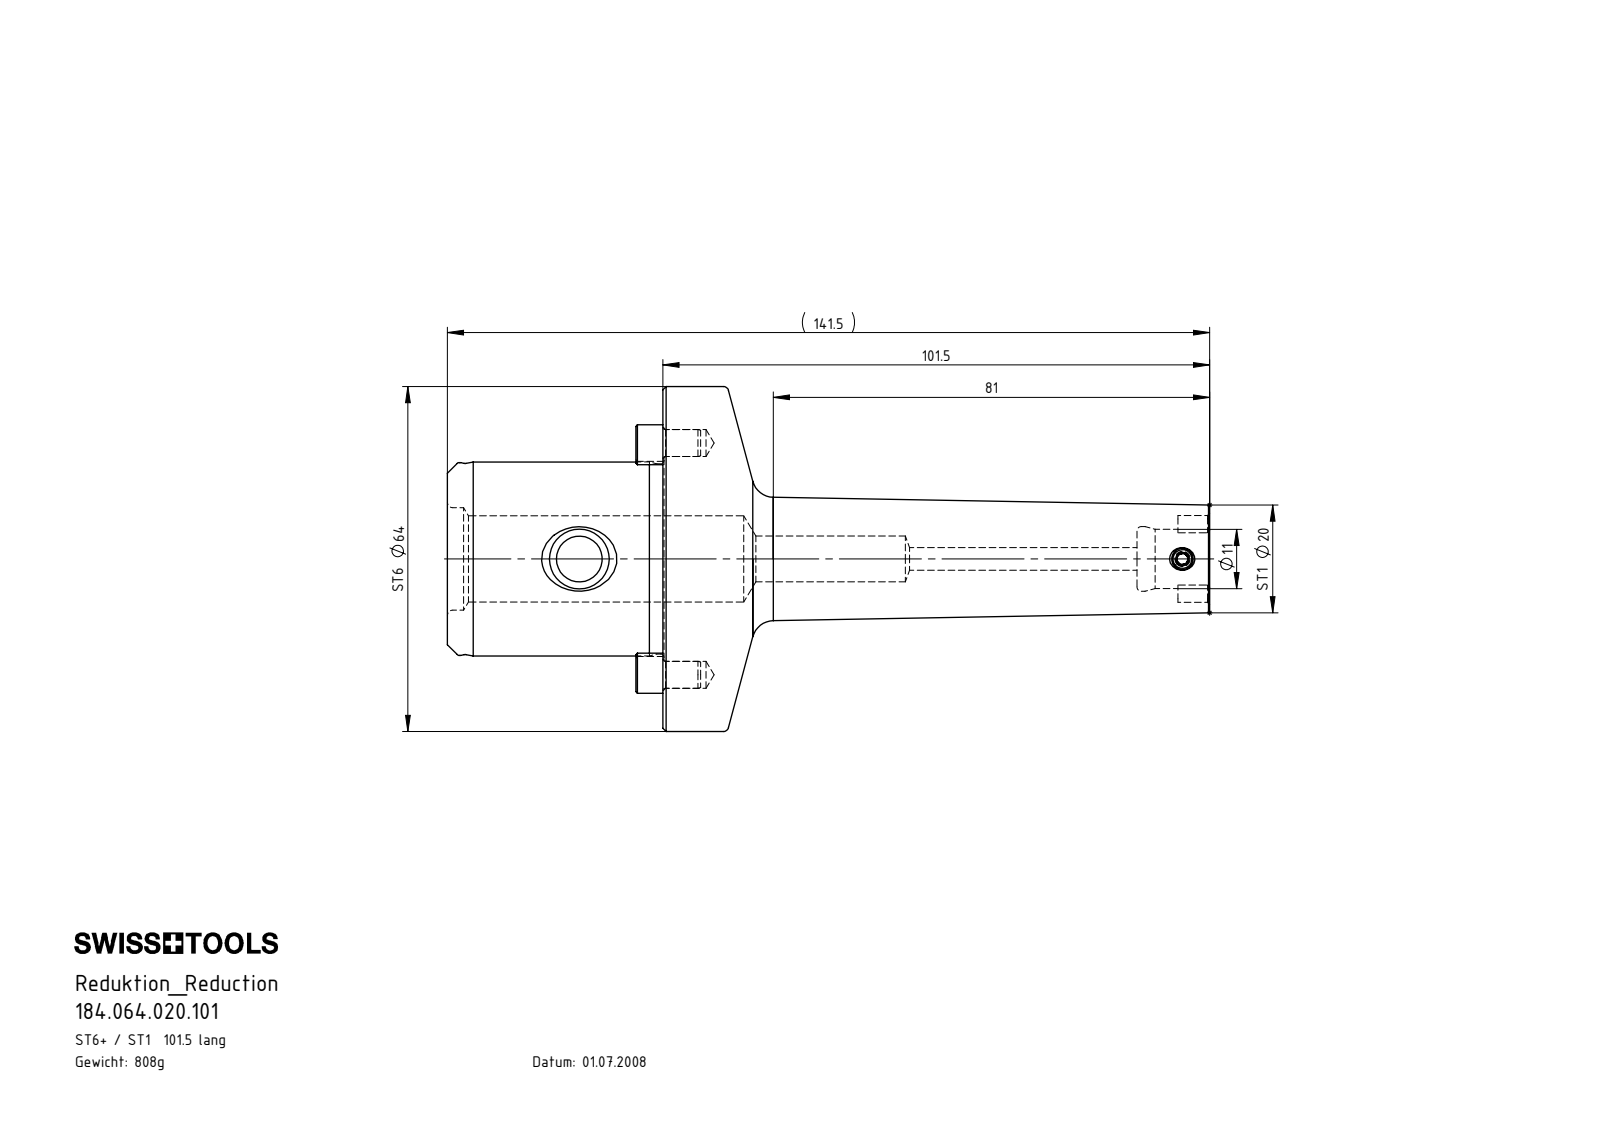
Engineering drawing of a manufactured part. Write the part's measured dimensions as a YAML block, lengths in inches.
part_name: "ST1-ER1.001.005_A; ST6-ER2.001.012_A; ST6-ST1.K01.101; ST6-ST1.K01.101_A"
step_written_by: "SolidWorks 2015 (CONFIG_CONTROL_DESIGN)"
units: inches
bodies: {solids: 4, faces: 166, planar: 26, cylindrical: 47, other: 93}
overall_size: [5.571, 2.52, 2.52]
volume: 6.355
surface_area: 37.52
round_holes:
  - {diameter: 0.197, count: 2}
  - {diameter: 0.138, count: 1}
  - {diameter: 0.165, count: 1}
  - {diameter: 0.335, count: 1}
  - {diameter: 0.433, count: 1}
  - {diameter: 0.472, count: 1}
  - {diameter: 0.63, count: 1}
  - {diameter: 0.748, count: 1}
round_bosses_or_shafts:
  - {diameter: 2.52, count: 1}
  - {diameter: 1.417, count: 1}
  - {diameter: 1.409, count: 1}
  - {diameter: 1.39, count: 1}
  - {diameter: 0.157, count: 1}
partial_cylinders:
  - {radius: 0.02, count: 4}
  - {radius: 0.051, count: 2}
  - {radius: 0.215, count: 2}
  - {radius: 0.711, count: 2}
face_to_face_distances: [1.575, 5.571, 3.996, 0.197, 1.378, 4.193, 5.039, 3.661, 3.465, 0.531]
hole_center_spacings: [0.846, 1.693, 4.407]
